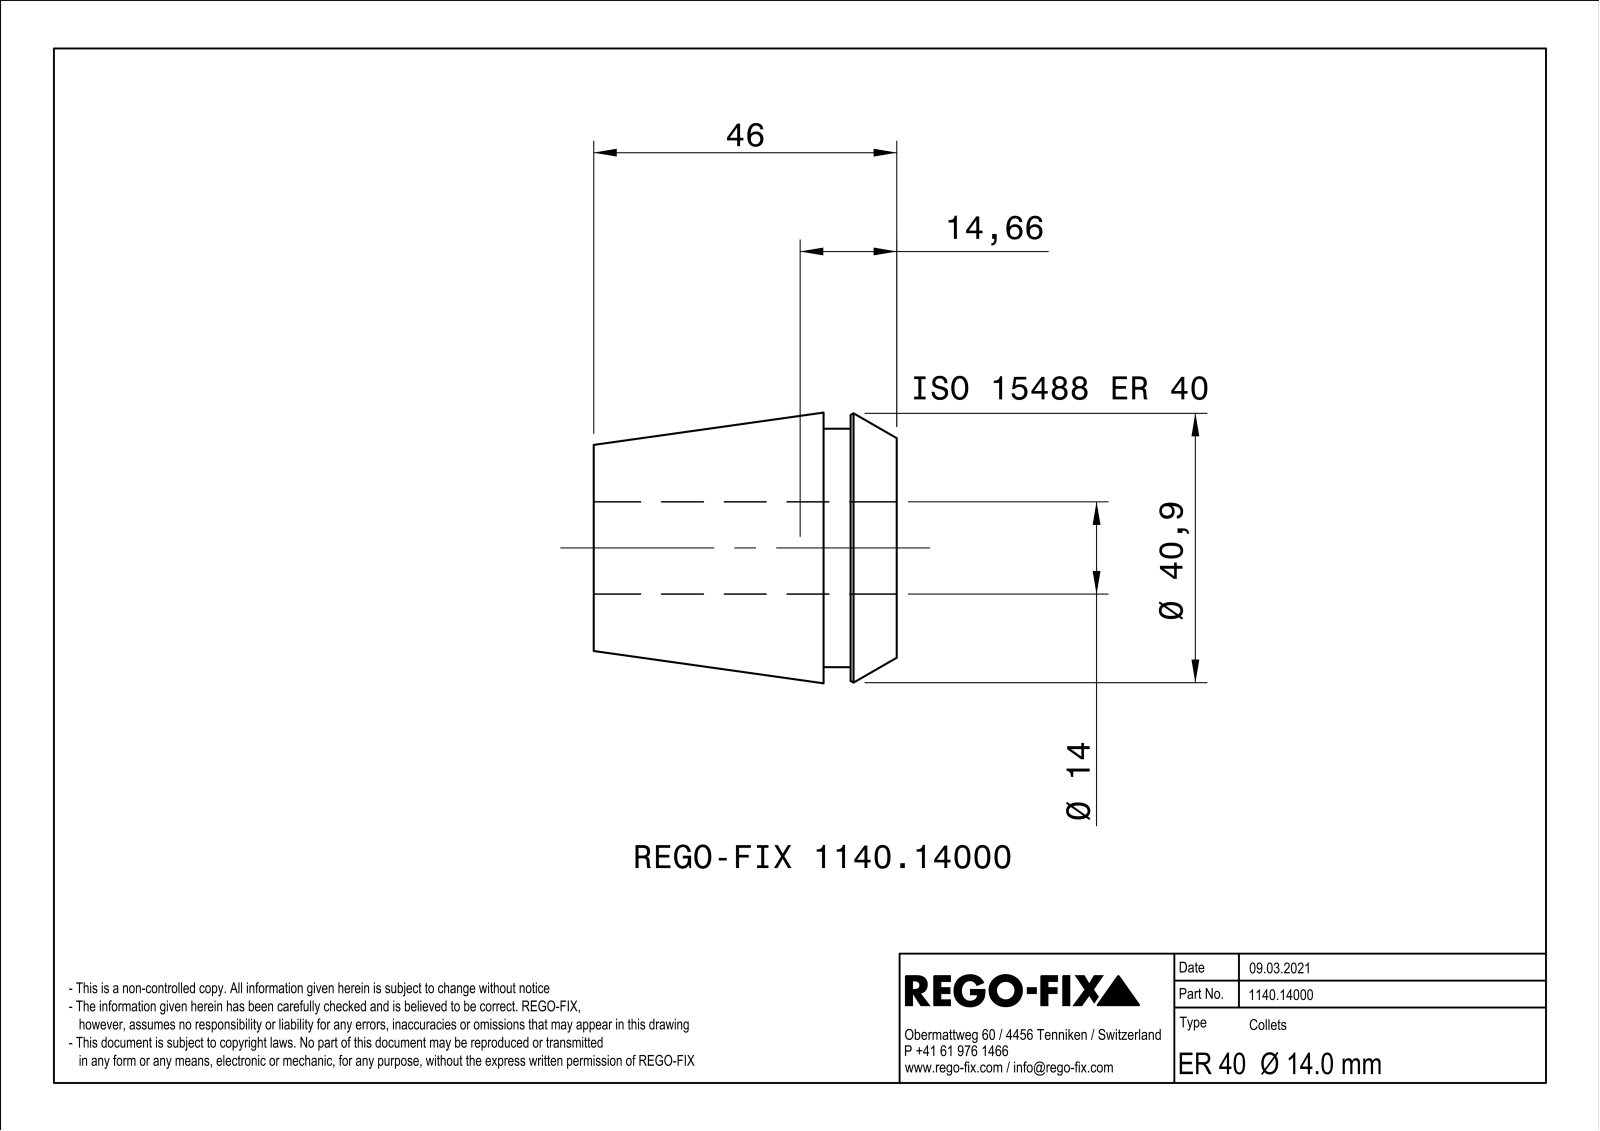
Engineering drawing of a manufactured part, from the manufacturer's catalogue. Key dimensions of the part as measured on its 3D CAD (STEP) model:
Part name (STEP PRODUCT): NOCUT
STEP written by: SIEMENS PLM Software Solid Edge ST10 (AUTOMOTIVE_DESIGN)
Units: millimetres
Bodies: 1 solid, 177 faces (88 planar, 9 cylindrical, 80 other)
Overall size (bounding box): 46 × 40.99 × 40.99
Volume: 33 494 mm³ · Surface area: 22 438 mm²
Round holes (diameter × count): ⌀14 ×1
Round bosses / shafts (diameter × count): ⌀36.2 ×1
Main face-to-face distances: 1, 46, 11.1, 34.9, 7, 4.1, 39, 7.5, 0.5, 3.6
